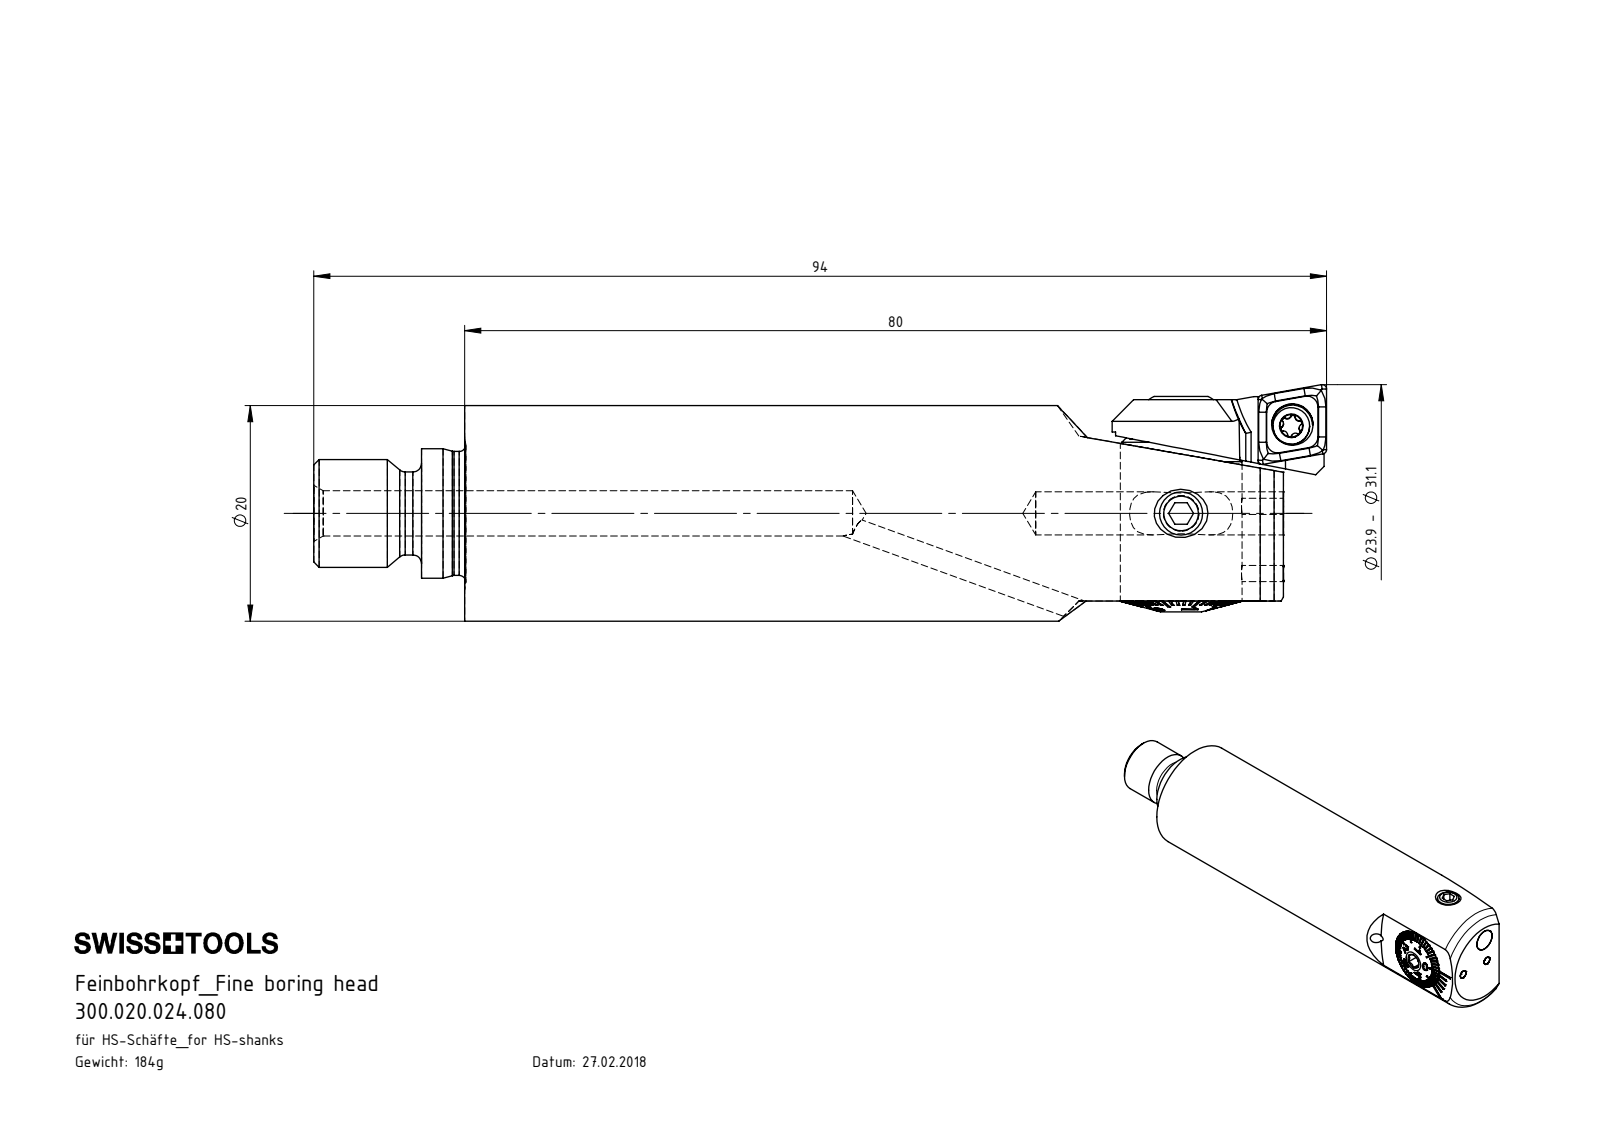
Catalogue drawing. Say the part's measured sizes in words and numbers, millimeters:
The part is named "ISO 4026 - M4 x 3; ISO 8744-1.5x5; HP1-F20.K10.080_A; F20-BG3.002.011_A (+7 more)". Its 3-D file was written by "SolidWorks 2017 (CONFIG_CONTROL_DESIGN)". It is 11 solids with 598 faces: 281 planar, 96 cylindrical and 221 other. Overall it measures 90 by 20 by 20 millimeters. Its volume is 22 759 cubic millimeters and its surface area 9 157 square millimeters. Round holes: 2 of diameter 1.4, 2 of diameter 3.3, 1 of diameter 0.5, 1 of diameter 1.5, 1 of diameter 2, 1 of diameter 3.75, 1 of diameter 4, 1 of diameter 4.2, 1 of diameter 4.5, 1 of diameter 5, 1 of diameter 6.6, 1 of diameter 7.05. Round bosses or shafts: 3 of diameter 1.5, 2 of diameter 4, 1 of diameter 20, 1 of diameter 12, 1 of diameter 11.5, 1 of diameter 11.3, 1 of diameter 11, 1 of diameter 10. Partial cylindrical surfaces (rounded edges, fillets, slot ends): 2 of radius 0.3, 2 of radius 1, 1 of radius 3.77. The main face-to-face distances are 76, 3.88, 1, 3.08, 0.8, 3.6, 11.15, 14.23, 15.03, 11.43. The hole center spacings are 0.75, 5, 5.58, 7.49.
